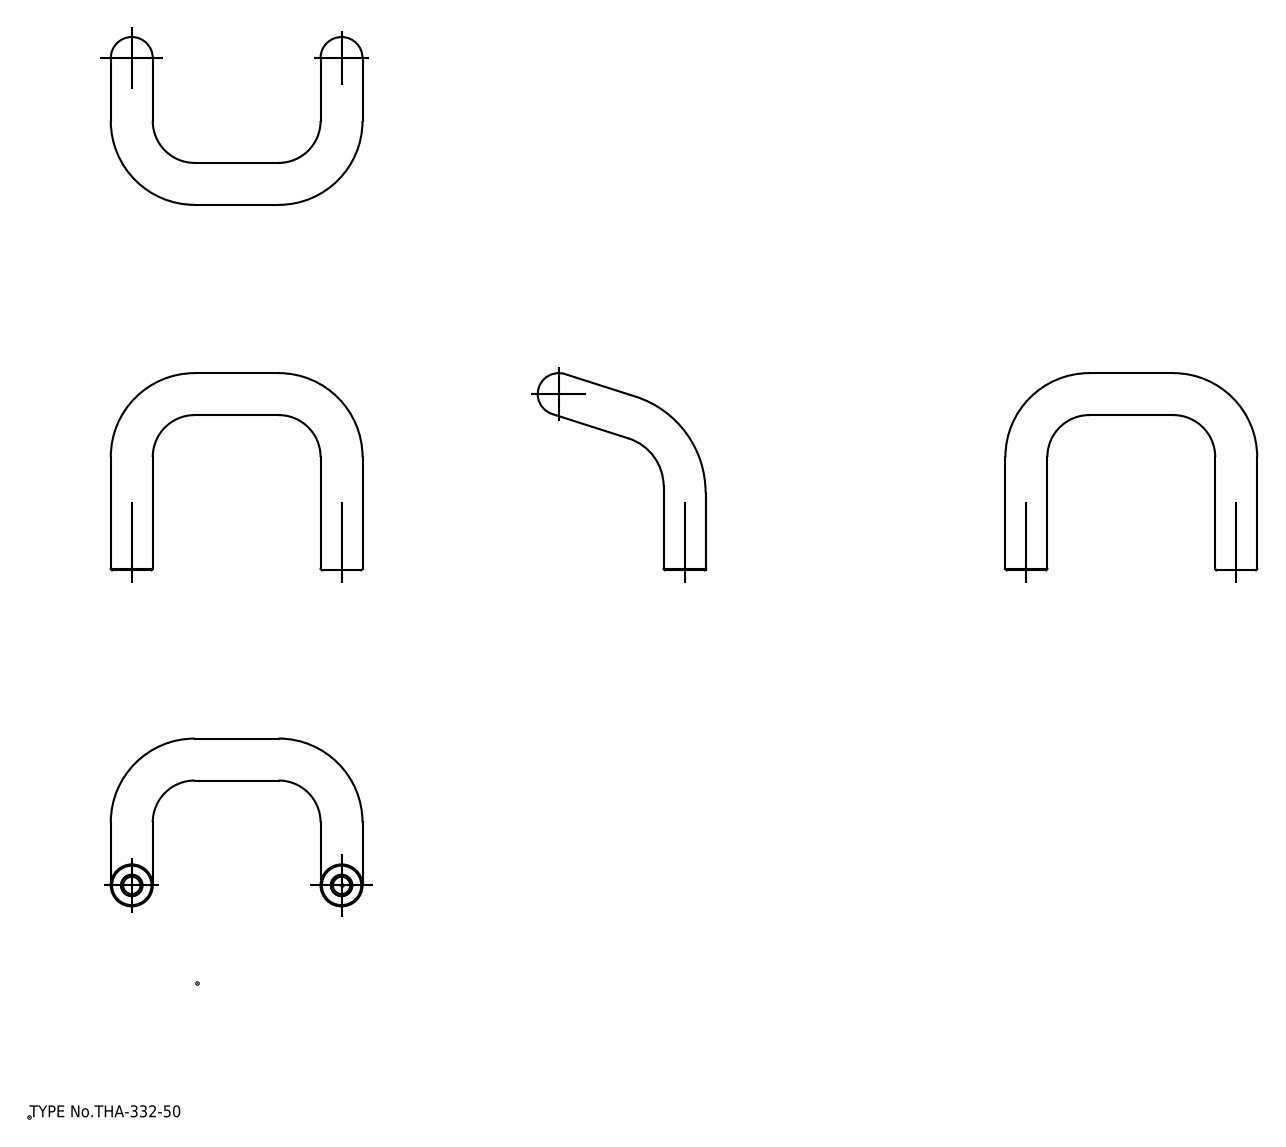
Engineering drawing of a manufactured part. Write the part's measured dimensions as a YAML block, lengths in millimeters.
step_written_by: "spGate 19.8.4 (****-****-****-****) (AUTOMOTIVE_DESIGN)"
units: millimeters
bodies: {solids: 1, faces: 38, planar: 4, cylindrical: 16, other: 18}
overall_size: [60, 47, 40]
volume: 11867
surface_area: 5402
round_holes:
  - {diameter: 5, count: 2}
round_bosses_or_shafts:
  - {diameter: 10, count: 5}
partial_cylinders:
  - {radius: 12, count: 1}
face_to_face_distances: [10]
hole_center_spacings: [50]
